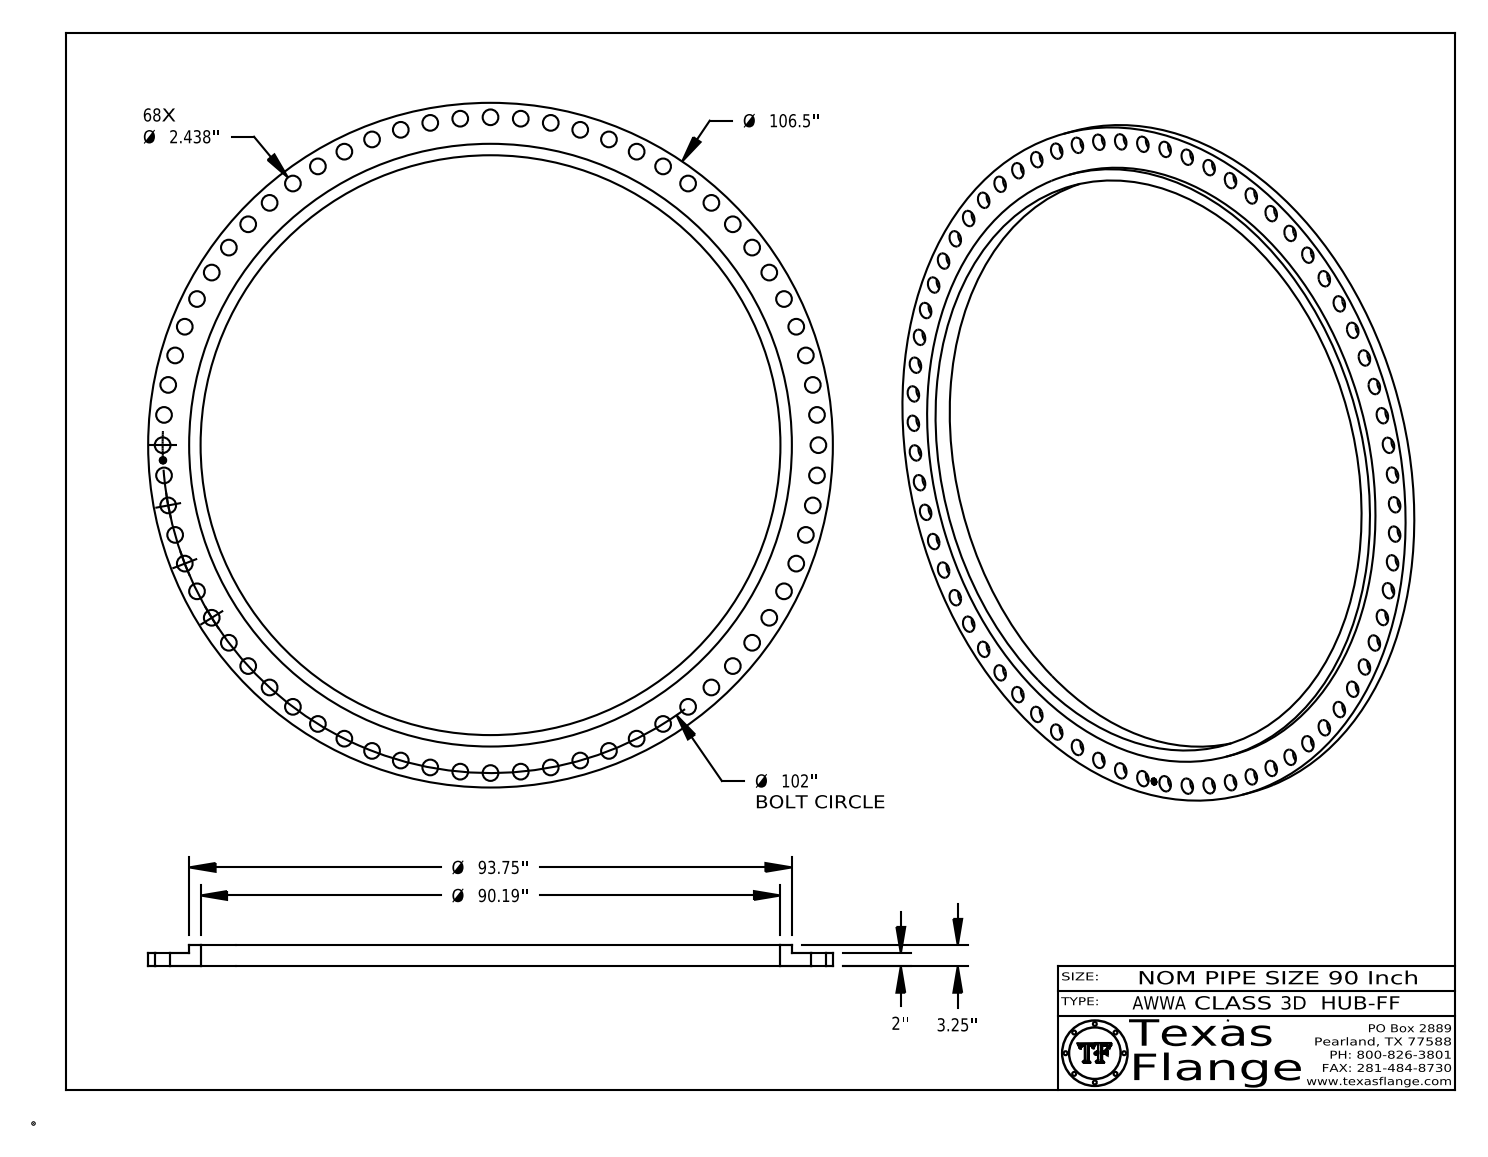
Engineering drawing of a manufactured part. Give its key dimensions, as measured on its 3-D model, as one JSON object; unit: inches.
{"part_name": "AWWA Class 3D-HUB-FF", "step_written_by": "CATIA V5 STEP AP214 (AUTOMOTIVE_DESIGN)", "units": "inches", "bodies": {"solids": 1, "faces": 530, "planar": 368, "cylindrical": 162, "other": 0}, "overall_size": [106.5, 106.5, 3.25], "volume_in3": 5047, "surface_area_in2": 7404, "round_holes": [[2.438, 68], [1, 1], [90.19, 1]], "round_bosses_or_shafts": [[0.061, 8], [106.5, 1], [93.75, 1], [0.788, 1]], "face_to_face_distances": [2, 3.25, 1.25, 0.015, 1.985, 1.265, 0.019, 0.298, 0.292, 0.054], "hole_center_spacings": [51, 9.411, 18.743, 4.711, 23.353, 14.092, 32.415, 41.2]}
